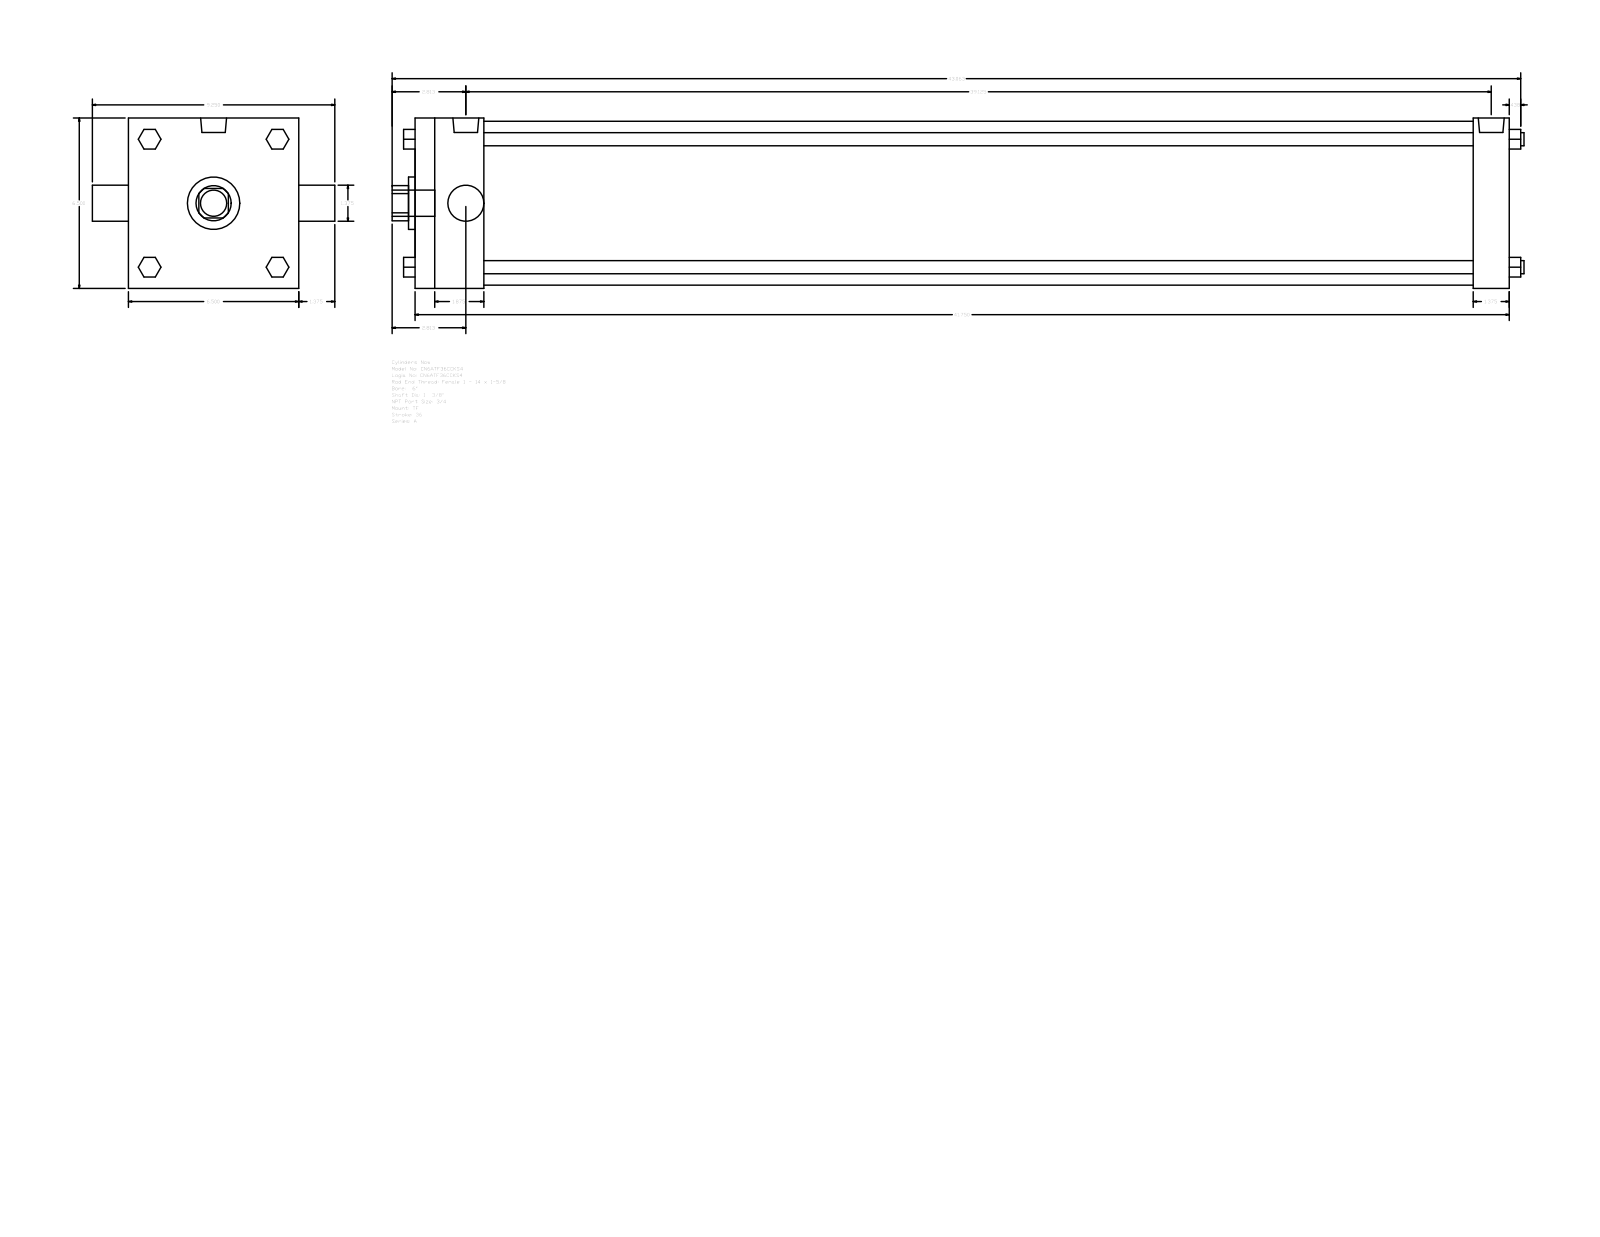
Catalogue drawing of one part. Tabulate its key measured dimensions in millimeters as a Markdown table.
| quantity | value |
| --- | --- |
| part name | A_TF__0600_1.375 |
| STEP written by | GSSL Pune (CONFIG_CONTROL_DESIGN) |
| units | millimeters |
| bodies | 0 solids, 120 faces (92 planar, 28 cylindrical, 0 other) |
| overall size | 1096.96 × 234.95 × 165.1 |
| round holes (diameter × count) | 34.92 × 2, 50.8 × 1, 158.75 × 1 |
| round bosses / shafts (diameter × count) | 12.7 × 4, 15.08 × 3, 25.12 × 2, 25.4 × 1 |
| partial cylindrical surfaces (radius × count) | 17.06 × 1 |
| main face-to-face distances | 165.1, 1060.44, 34.92, 66.67, 993.77, 1025.52, 958.85, 19.05, 61.97, 107.34 |
